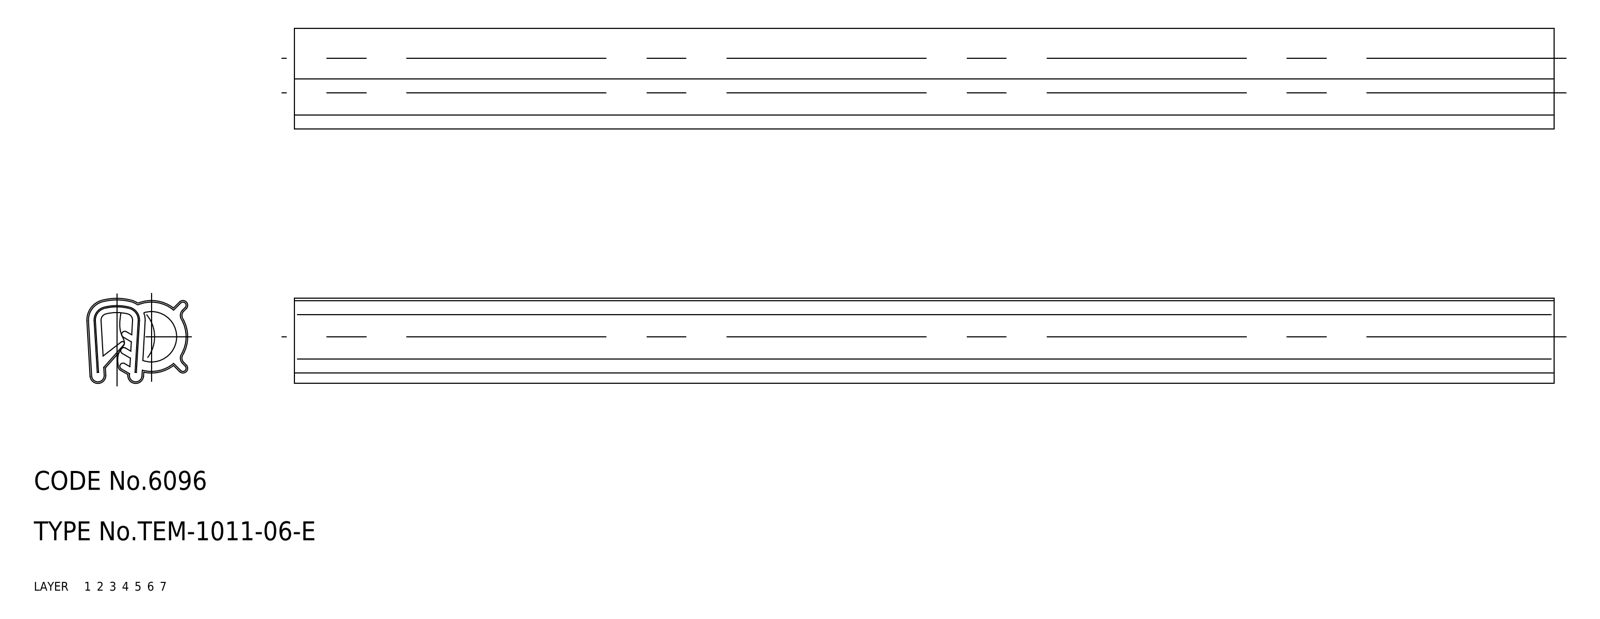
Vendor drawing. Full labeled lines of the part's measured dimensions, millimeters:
Part name (STEP PRODUCT): sheet; rubber foam; gasket; center core (+1 more)
STEP written by: CADfix (AUTOMOTIVE_DESIGN)
Units: millimetres
Bodies: 4 solids, 123 faces (0 planar, 0 cylindrical, 123 other)
Overall size (bounding box): 200 × 16 × 13.5
Volume: 22 872 mm³ · Surface area: 73 952 mm²
